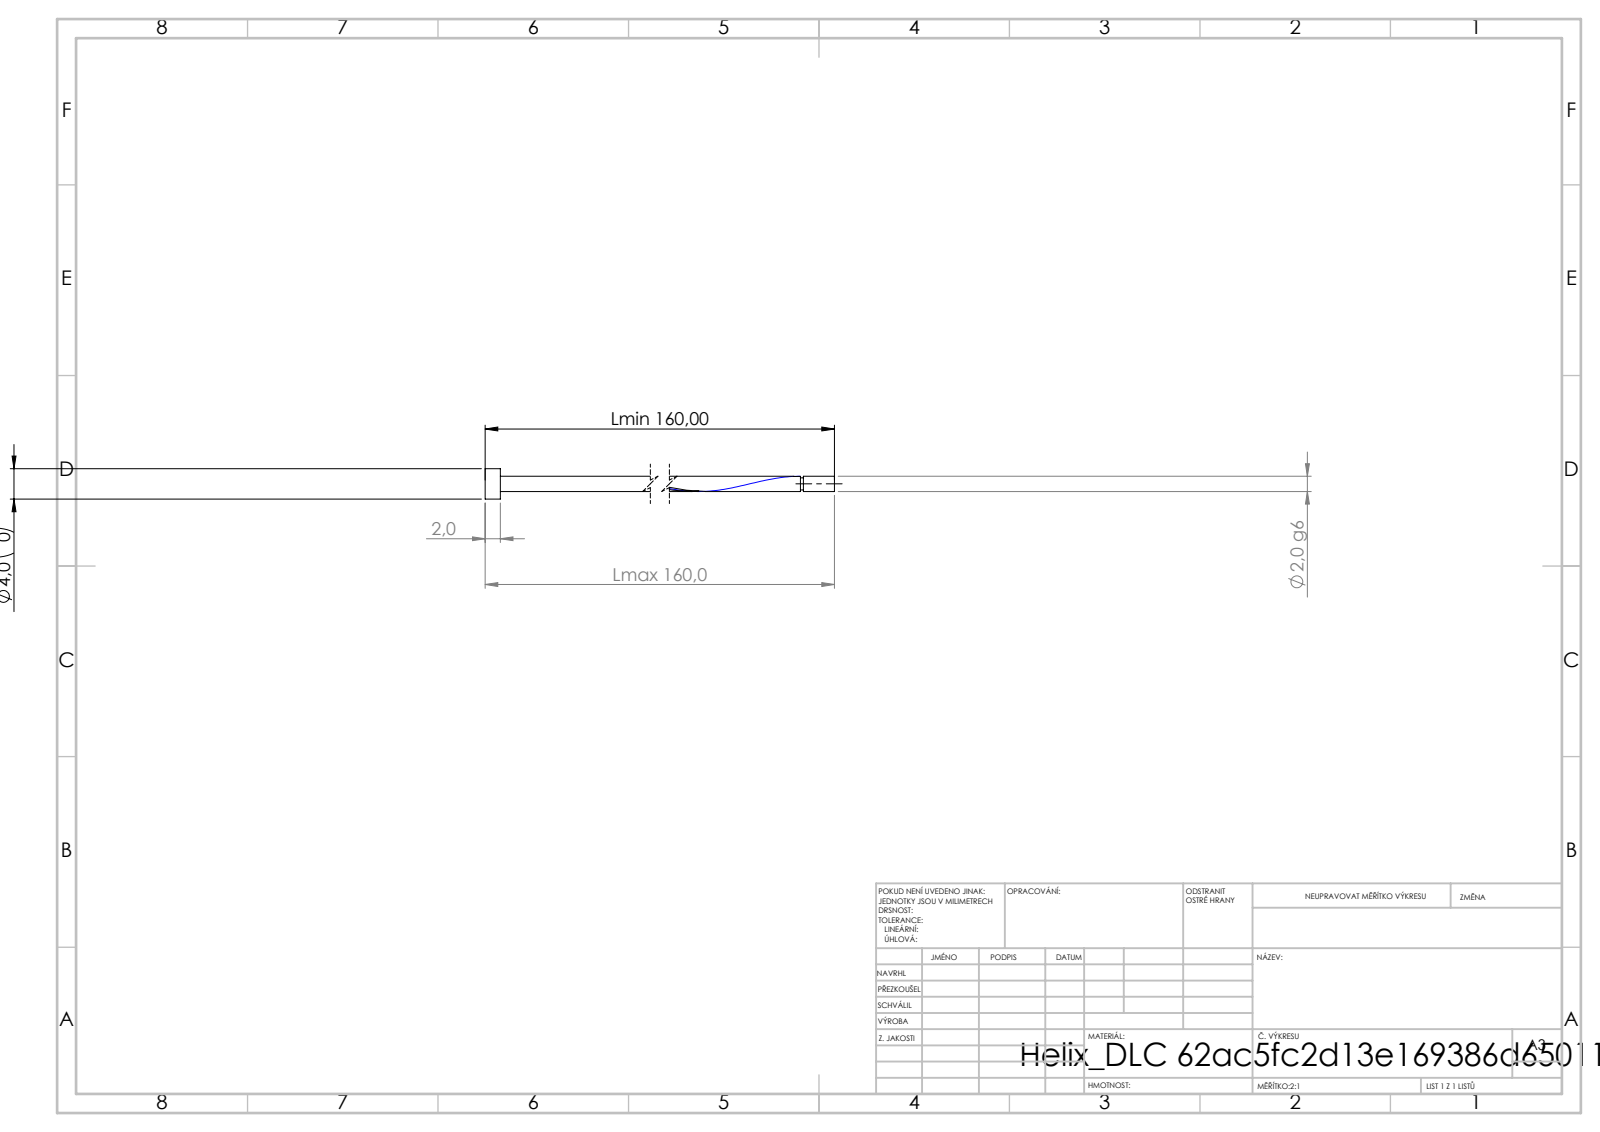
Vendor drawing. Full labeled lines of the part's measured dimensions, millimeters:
STEP written by: SolidWorks 2019 (CONFIG_CONTROL_DESIGN)
Units: millimetres
Bodies: 1 solid, 16 faces (6 planar, 9 cylindrical, 1 other)
Overall size (bounding box): 160 × 4 × 4
Volume: 628 mm³ · Surface area: 1 395 mm²
Round bosses / shafts (diameter × count): ⌀4 ×1, ⌀2 ×1, ⌀1.6 ×1
Main face-to-face distances: 2, 160, 158, 155.93, 153.93, 4.07, 155.53, 153.53, 0.4, 4.47
